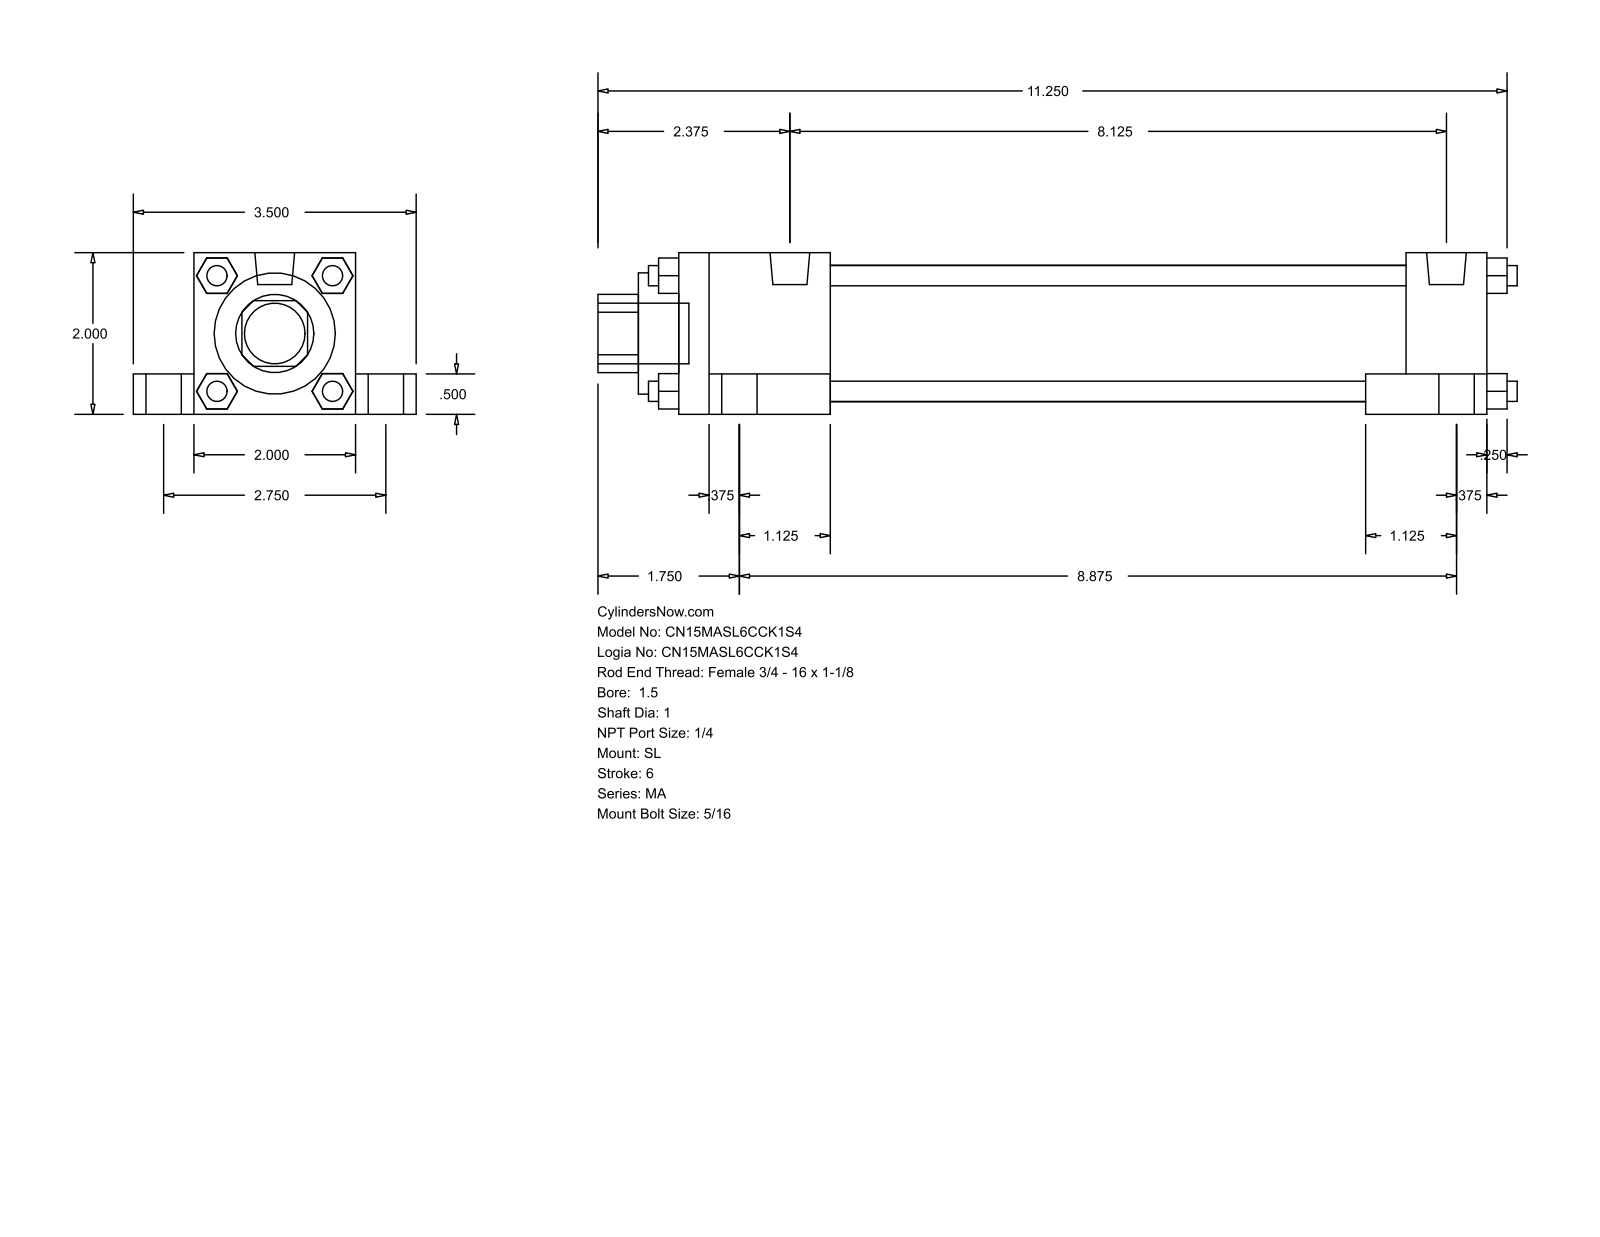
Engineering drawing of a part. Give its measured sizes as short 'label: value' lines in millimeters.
name: MA_SL__0150_1
written by: GSSL Pune (CONFIG_CONTROL_DESIGN)
unit: mm
bodies: 0 solids, 148 faces (112 planar, 36 cylindrical, 0 other)
size: 288.93 × 88.9 × 50.8
holes: 1× ⌀25.4, 1× ⌀38.1, 1× ⌀42.93
bosses: 4× ⌀17.46, 4× ⌀11.11, 4× ⌀7.94, 4× ⌀6.35, 2× ⌀12.49, 1× ⌀19.05
rounds: 1× R12.29
face distances: 50.8, 12.7, 19.05, 69.85, 9.52, 38.1, 6.35, 254, 25.4, 228.6
